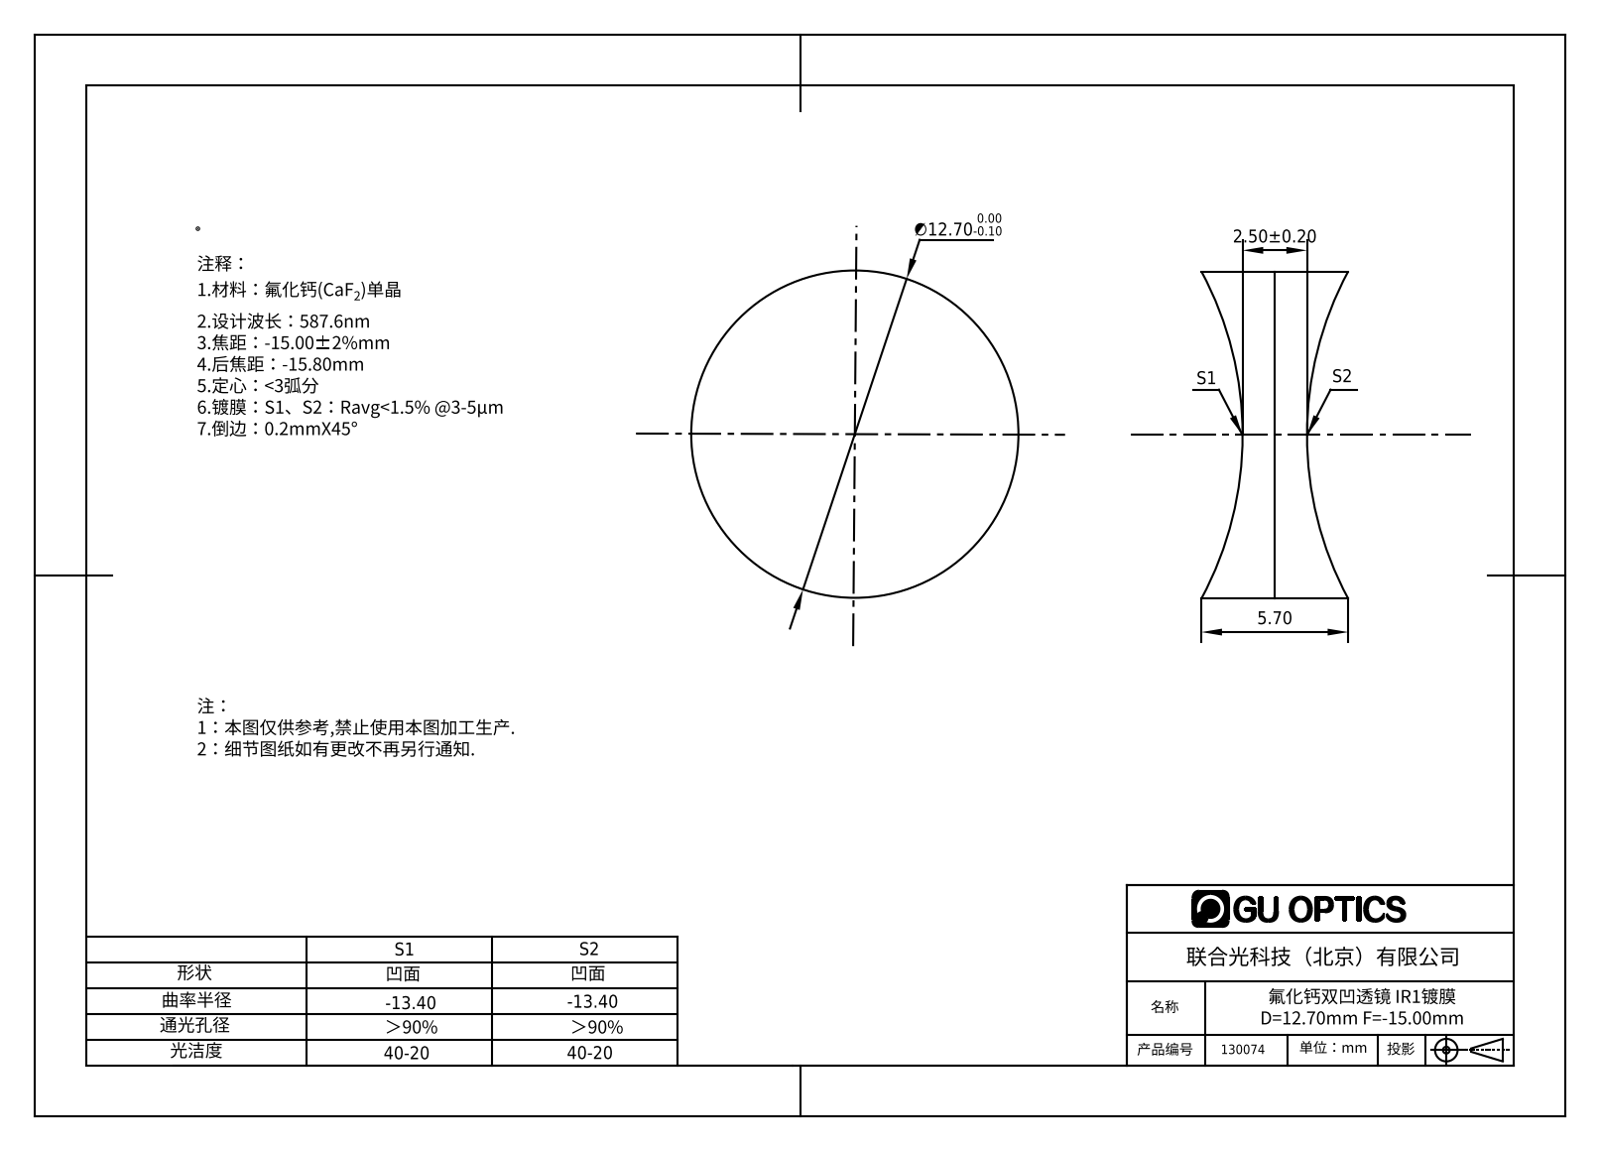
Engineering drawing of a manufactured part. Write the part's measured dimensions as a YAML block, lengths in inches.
part_name: "130070"
step_written_by: "SolidWorks 2016 (AUTOMOTIVE_DESIGN)"
units: inches
bodies: {solids: 1, faces: 6, planar: 0, cylindrical: 2, other: 4}
overall_size: [0.5, 0.5, 0.224]
volume: 0.031
surface_area: 0.77
round_bosses_or_shafts:
  - {diameter: 0.5, count: 1}
